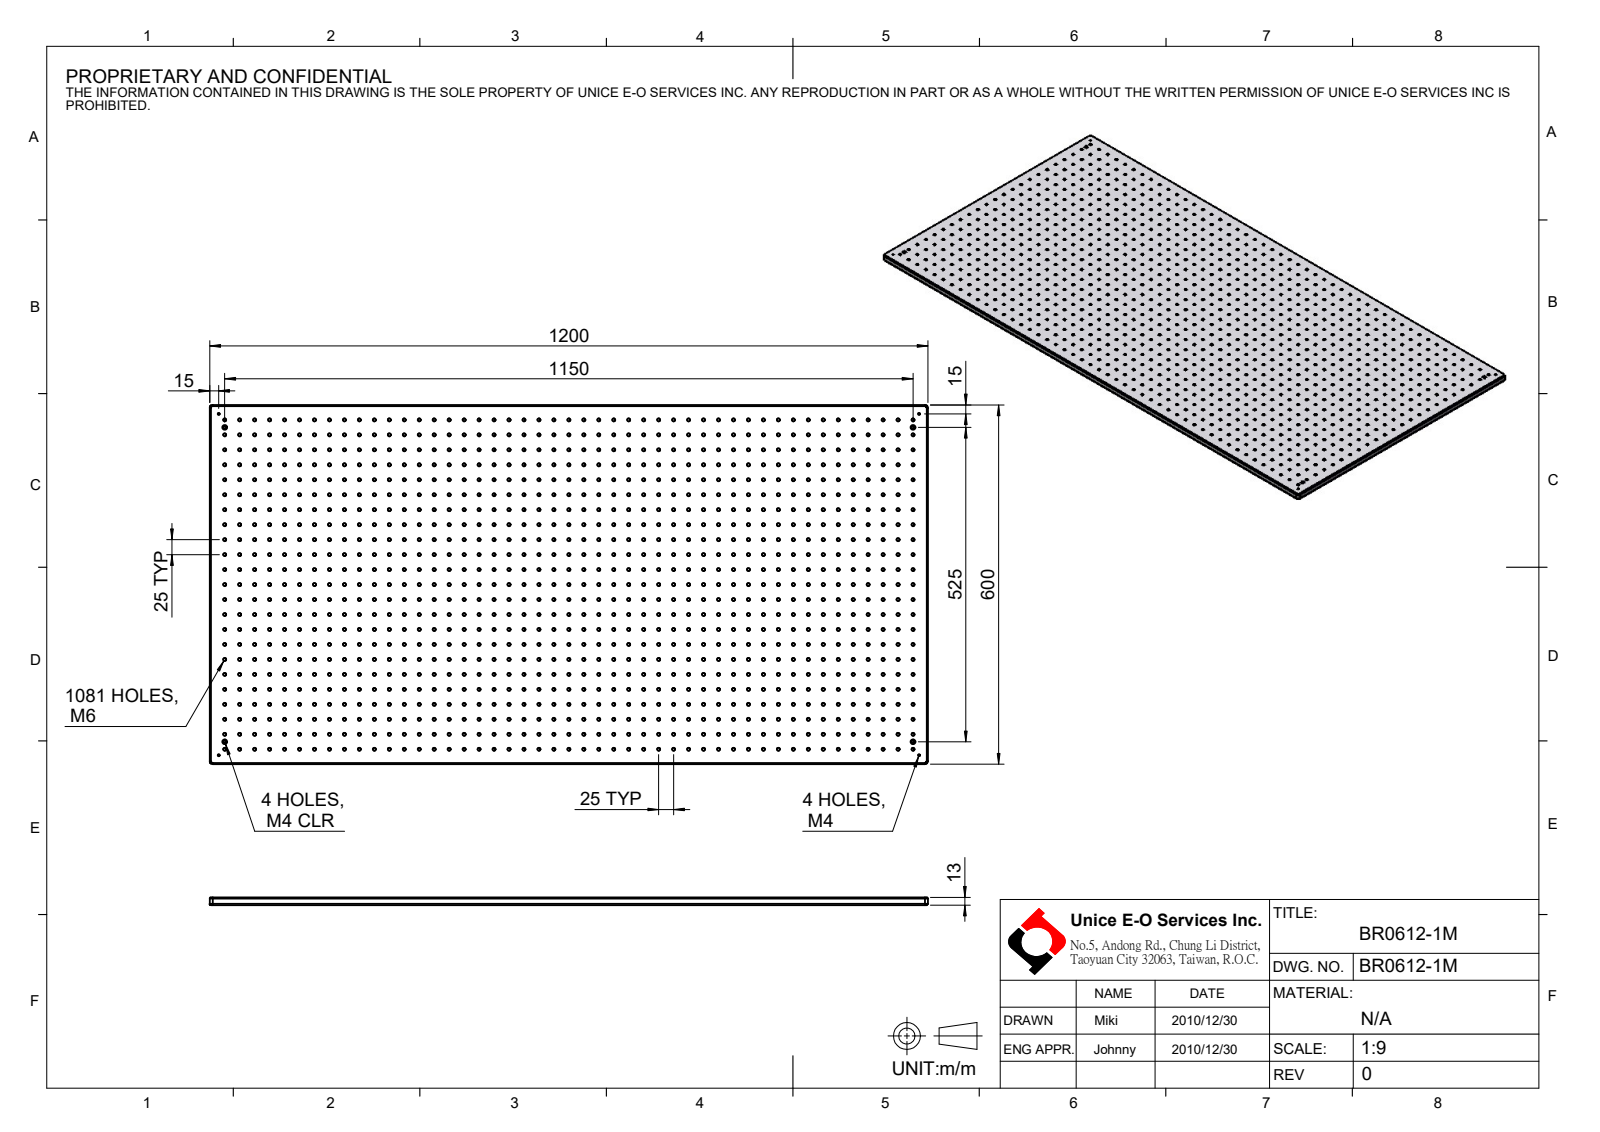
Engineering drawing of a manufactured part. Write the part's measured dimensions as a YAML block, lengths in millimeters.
part_name: "BR0612-1M"
step_written_by: "SolidWorks 2016 (CONFIG_CONTROL_DESIGN)"
units: millimeters
bodies: {solids: 1, faces: 2216, planar: 10, cylindrical: 2198, other: 8}
overall_size: [1200, 600, 13]
volume: 9076000
surface_area: 1660000
round_holes:
  - {diameter: 5, count: 1081}
  - {diameter: 3.3, count: 4}
  - {diameter: 4.5, count: 4}
  - {diameter: 8, count: 4}
partial_cylinders:
  - {radius: 2, count: 8}
  - {radius: 5, count: 4}
face_to_face_distances: [13, 600, 1200, 7, 6]
hole_center_spacings: [25, 50, 75, 100, 125, 150, 175, 200]
